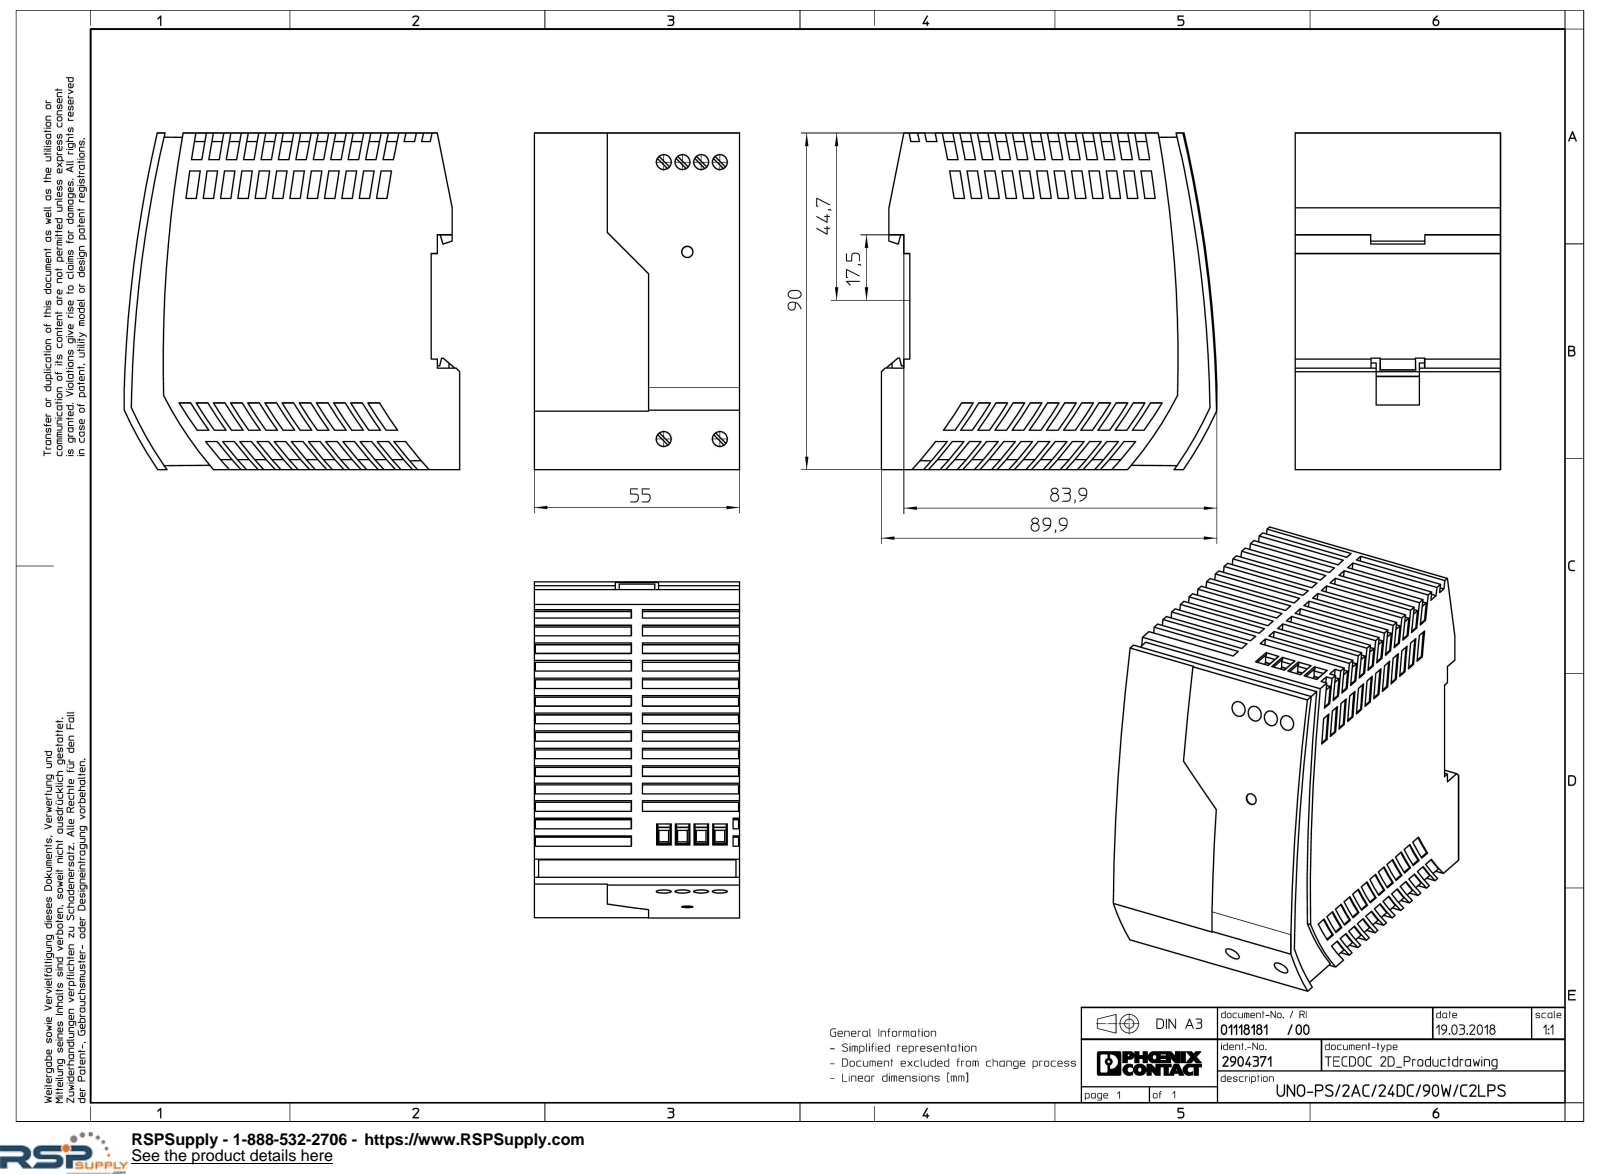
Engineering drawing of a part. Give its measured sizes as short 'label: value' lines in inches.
name: UNO_PS_2AC_24DC90W_C2LPS-select
written by: Creo Elements/Direct Modeling 20.1A 29-Sep-2018 (C) Parametric Technology GmbH (AUTOMOTIVE_DESIGN)
unit: in
bodies: 1 solid, 779 faces (558 planar, 219 cylindrical, 2 other)
size: 3.543 × 3.538 × 2.165
volume: 24.14 in³; area: 68.19 in²
holes: 6× ⌀0.157
rounds: 26× R4.37, 1× R3.858, 1× R3.88, 1× R3.937, 1× R11.128, 1× R11.217, 1× R11.29, 1× R11.471
face distances: 2.165, 0.091, 3.453, 3.543, 0.106, 3.346, 3.437, 2.154, 0.299, 2.142
hole spacings: 0.197, 0.394, 2.913, 2.92, 0.591, 0.592, 2.94, 2.94
